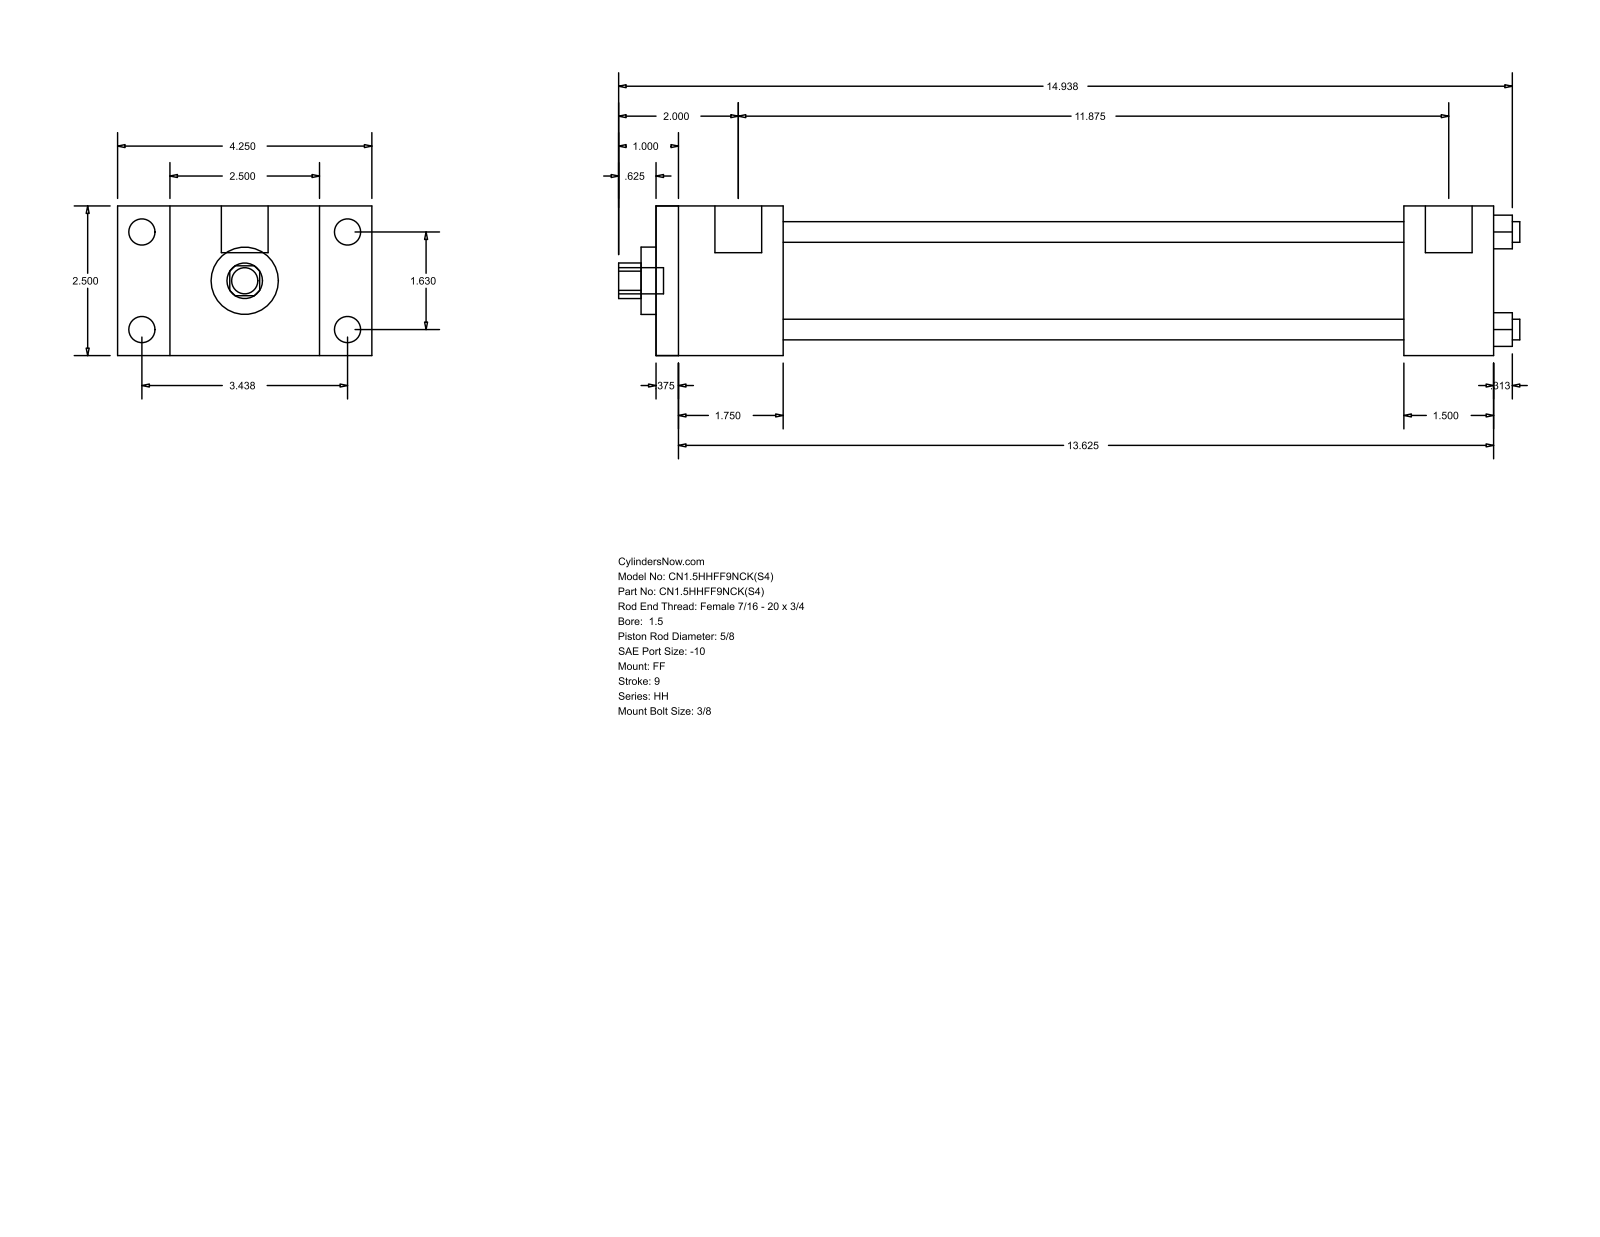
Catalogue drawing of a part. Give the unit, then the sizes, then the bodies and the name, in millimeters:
Units: millimetres
Overall size (bounding box): 382.59 × 107.95 × 63.5
Round holes (diameter × count): ⌀8.76 ×4, ⌀15.88 ×1, ⌀28.57 ×1, ⌀44.45 ×1
Round bosses / shafts (diameter × count): ⌀11.13 ×4, ⌀5.56 ×4, ⌀19.84 ×2, ⌀11.11 ×1
Partial cylindrical surfaces — rounded edges, fillets, slot ends (radius × count): R7.54 ×1
Main face-to-face distances: 63.5, 355.6, 9.52, 38.1, 346.08, 53.97, 44.45, 301.63, 317.5, 307.98
Hole centre spacings: 29.27, 41.4, 58.55
Bodies: 0 solids, 92 faces (64 planar, 28 cylindrical, 0 other)
Part name (STEP PRODUCT): HH_FF__0150_0.625
STEP written by: GSSL Pune (CONFIG_CONTROL_DESIGN)
